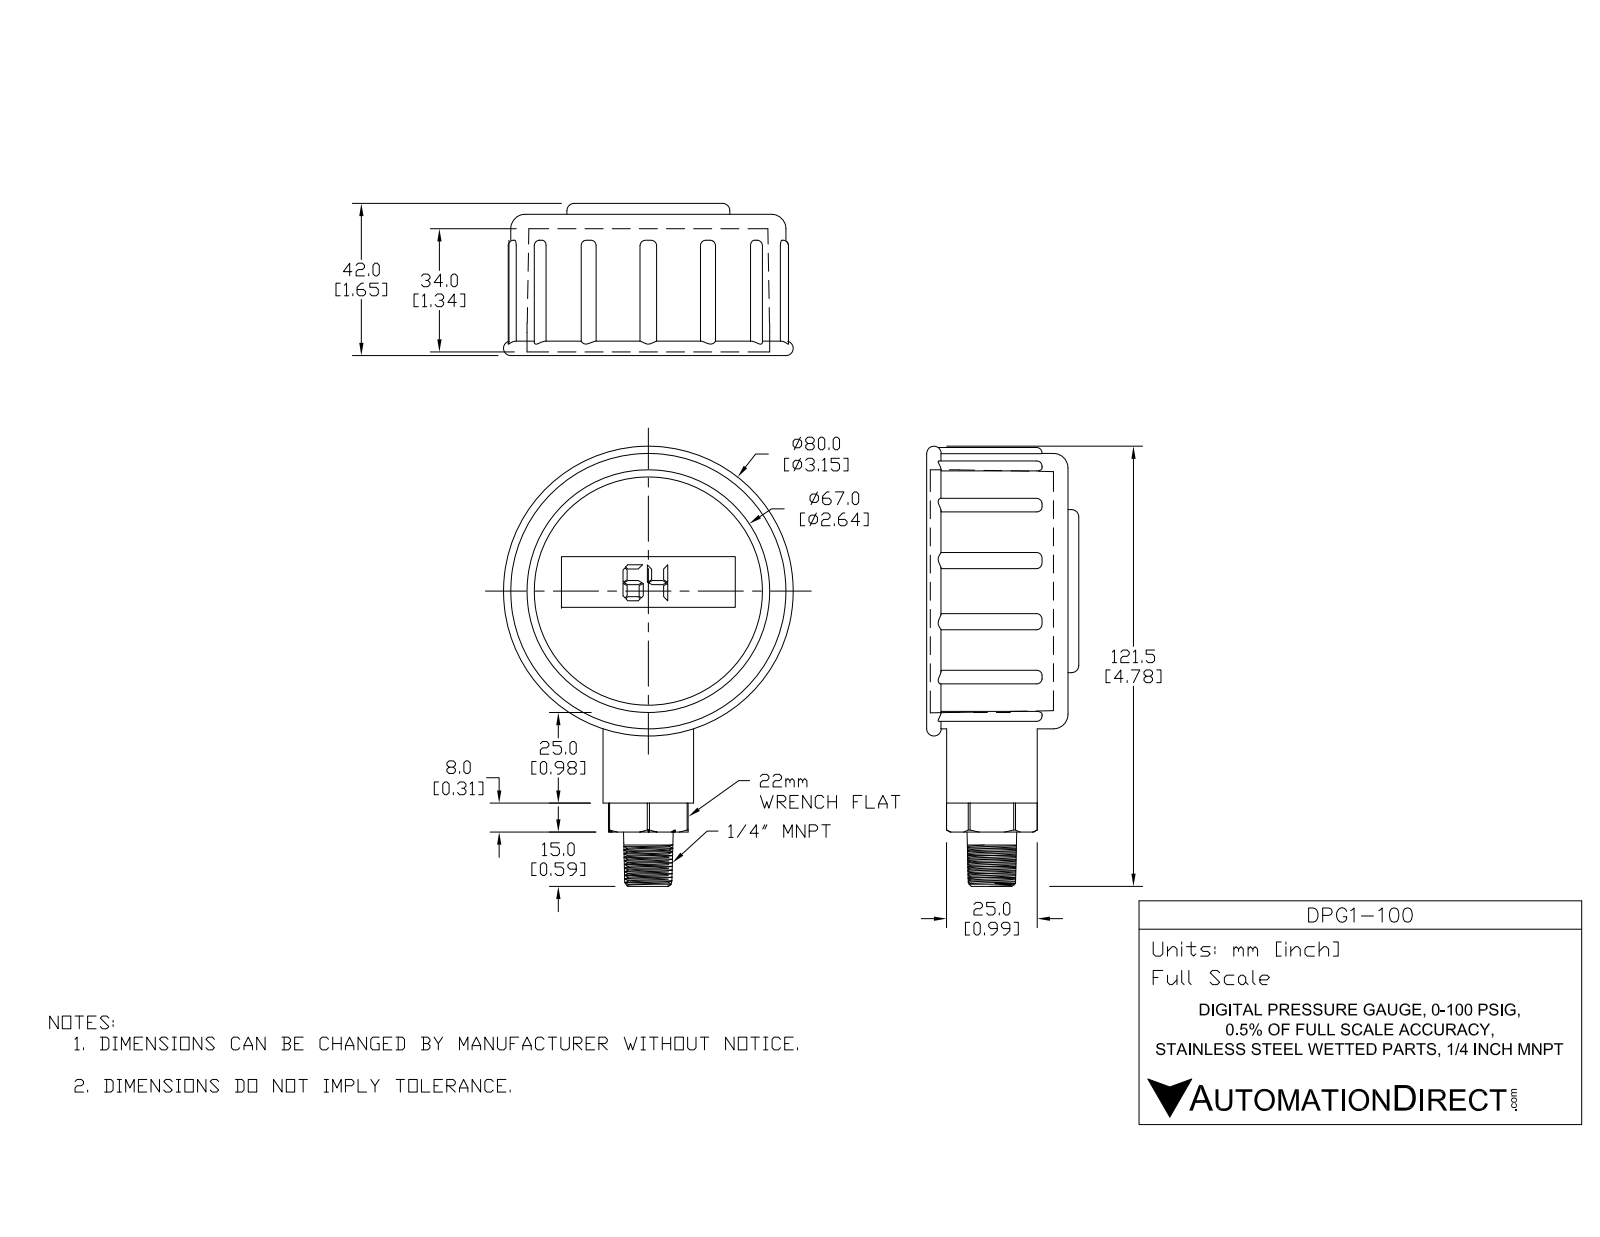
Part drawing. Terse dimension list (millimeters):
name: DPG1-100
written by: SolidWorks 2021 (CONFIG_CONTROL_DESIGN)
unit: mm
bodies: 4 solids, 181 faces (71 planar, 49 cylindrical, 61 other)
size: 121.62 × 80 × 42
volume: 196 180 mm³; area: 45 978 mm²
holes: 1× ⌀63, 1× ⌀67.19
bosses: 1× ⌀76, 1× ⌀67, 1× ⌀45, 1× ⌀25, 1× ⌀10
rounds: 13× R2.38, 6× R8.5, 1× R38
face distances: 33.95, 4, 37.95, 3, 7, 40.95, 42, 39, 35, 1.05
